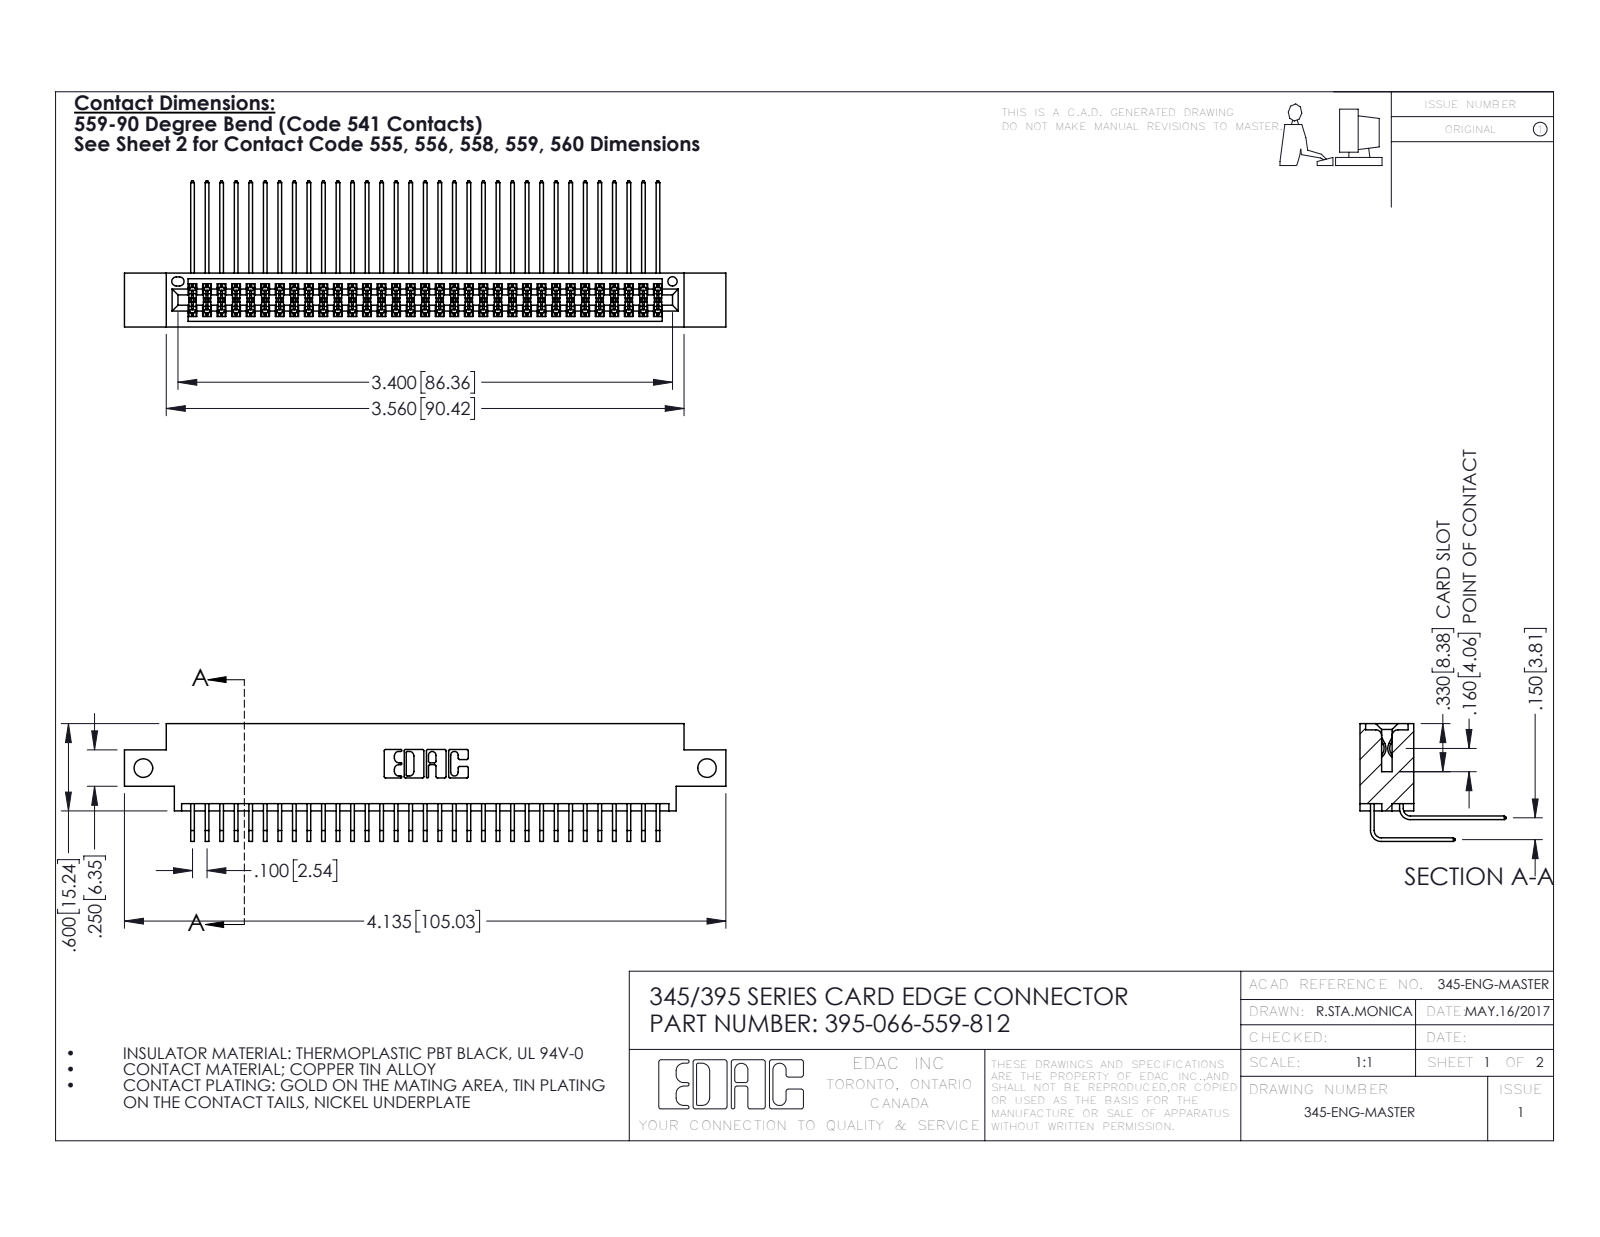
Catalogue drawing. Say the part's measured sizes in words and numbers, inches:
The part is named "345 Part_0.170 Offset - Side Mount; 345-292-001_558 559 Tail - 1; 345-292-001_559 Tail - 2; 395-066-559-812". Its 3-D file was written by "SolidWorks 2016 (CONFIG_CONTROL_DESIGN)". It is 67 solids with 3562 faces: 2394 planar, 1168 cylindrical and 0 other. Overall it measures 4.135 by 1.005 by 0.809 inches. Its volume is 0.628 cubic inches and its surface area 26.11 square inches. Round holes: 2 of diameter 0.128, 1 of diameter 0.064. Partial cylindrical surfaces (rounded edges, fillets, slot ends): 100 of radius 0.006, 22 of radius 0.01, 6 of radius 0.007, 6 of radius 0.031, 3 of radius 0.026, 2 of radius 0.014, 2 of radius 0.019, 2 of radius 0.022. The main face-to-face distances are 0.072, 0.298, 0.37, 0.2, 0.098, 0.272, 0.025, 0.225, 0.15, 0.175. The hole center spacings are 3.875.
